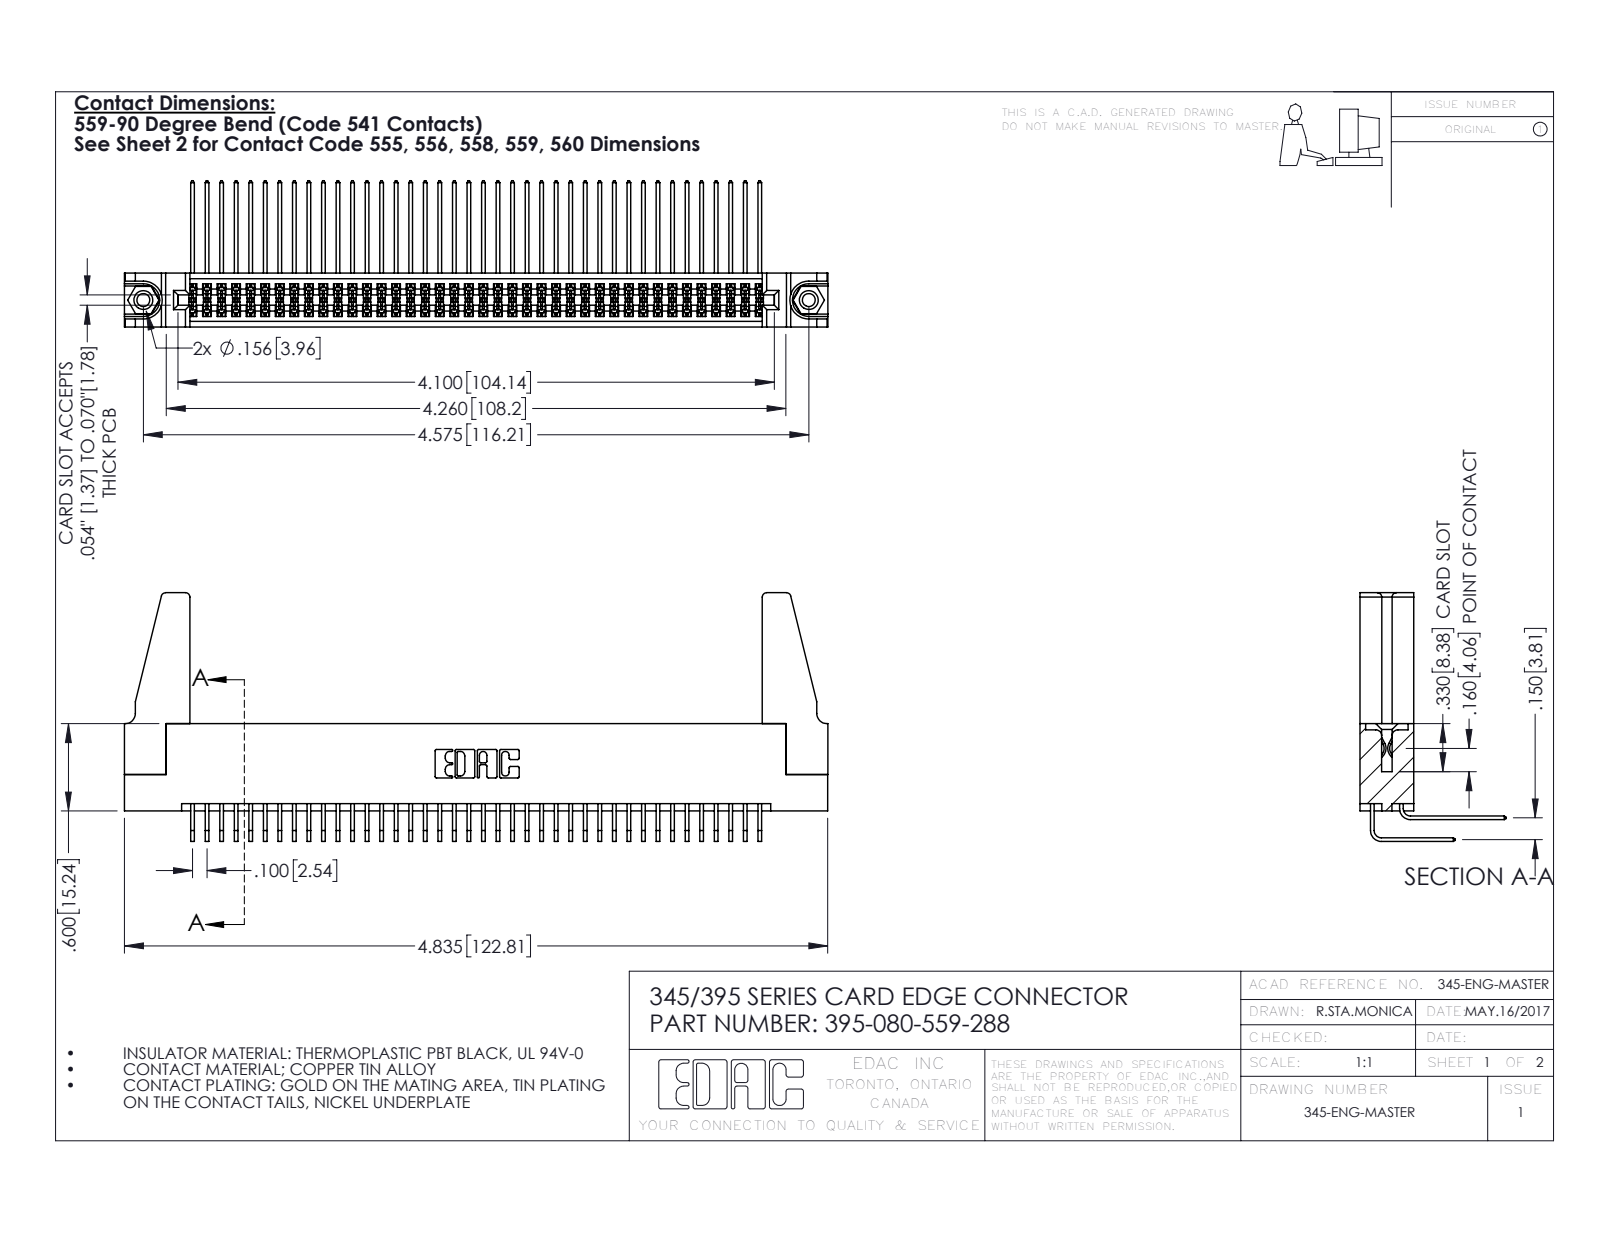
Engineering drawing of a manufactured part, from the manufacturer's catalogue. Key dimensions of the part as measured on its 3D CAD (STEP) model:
Part name (STEP PRODUCT): 345 Part_Flush Mounting Lugs - 0.156 Dia-TH; 345-292-001_558 559 Tail - 1; 345-292-001_559 Tail - 2; 345-220-078_345-220-088 (+2 more)
STEP written by: SolidWorks 2016 (CONFIG_CONTROL_DESIGN)
Units: inches
Bodies: 85 solids, 4410 faces (2952 planar, 1442 cylindrical, 16 other)
Overall size (bounding box): 4.836 × 1.709 × 1.005
Volume: 0.954 in³ · Surface area: 36.5 in²
Round holes (diameter × count): ⌀0.089 ×2, ⌀0.125 ×2, ⌀0.156 ×2, ⌀0.064 ×1
Round bosses / shafts (diameter × count): ⌀0.155 ×2
Partial cylindrical surfaces — rounded edges, fillets, slot ends (radius × count): R0.006 ×121, R0.01 ×22, R0.03 ×8, R0.007 ×6, R0.031 ×6, R0.026 ×3, R0.014 ×2, R0.019 ×2
Main face-to-face distances: 0.072, 0.298, 0.37, 0.2, 0.098, 0.272, 0.025, 0.225, 0.175, 0.15
Hole centre spacings: 0.27, 4.339, 4.575
